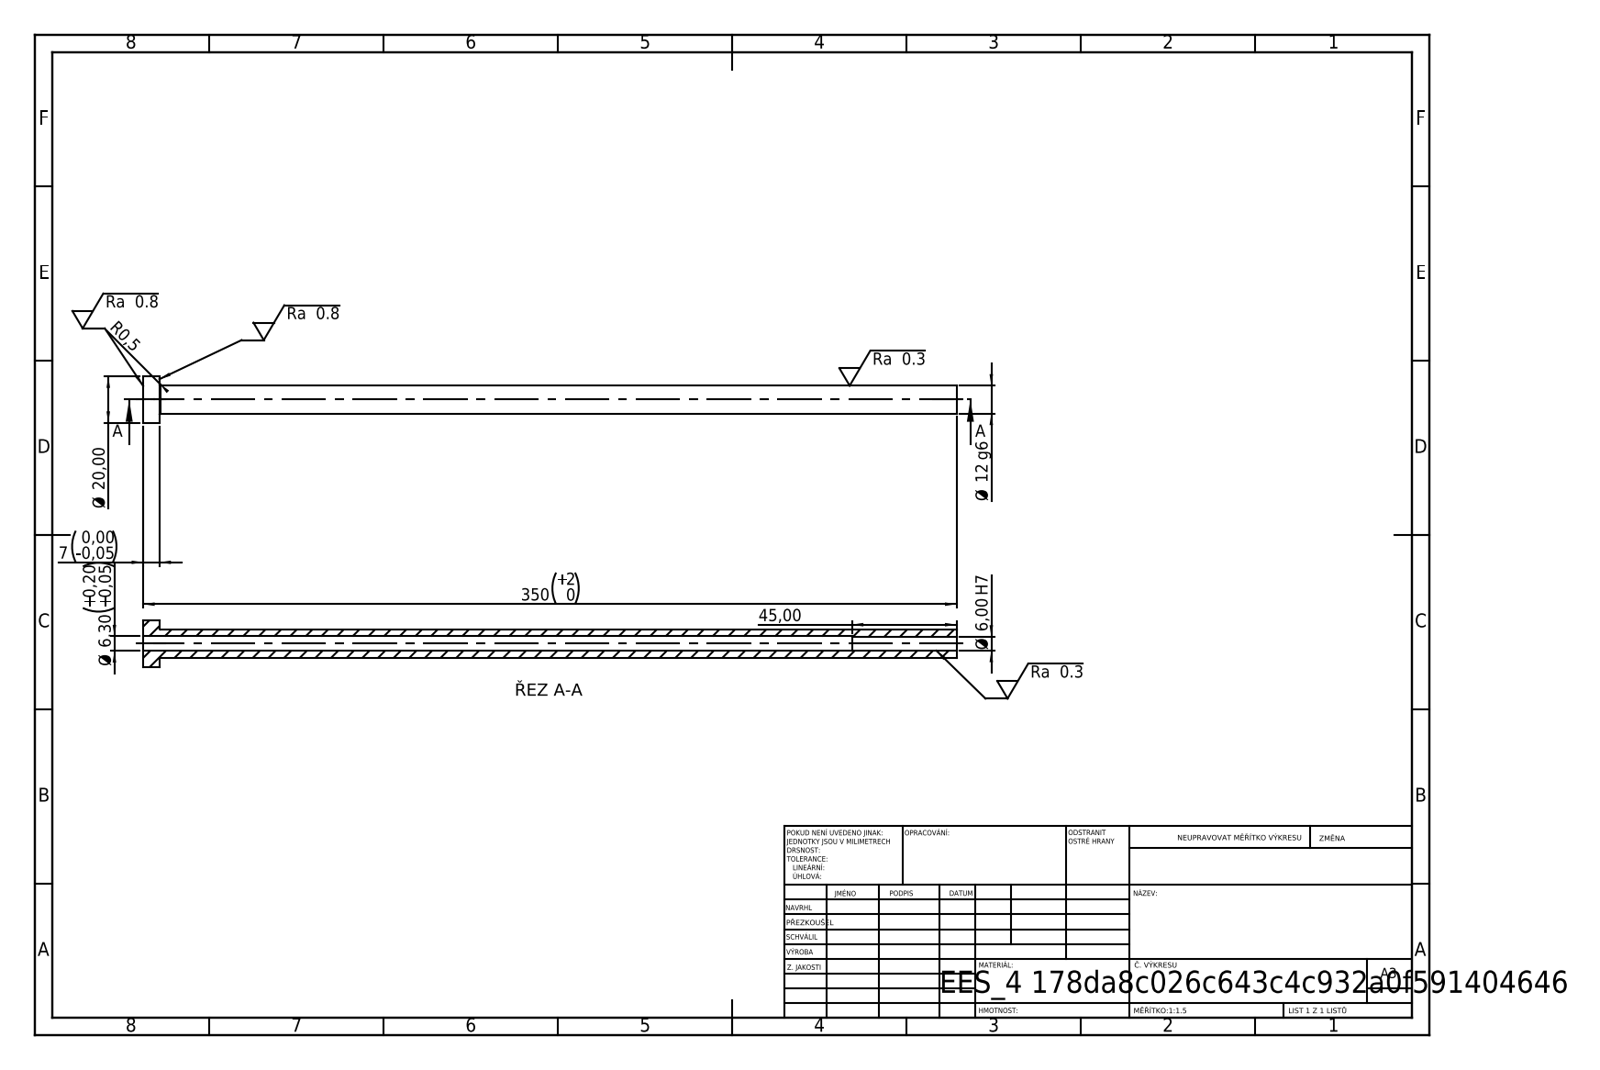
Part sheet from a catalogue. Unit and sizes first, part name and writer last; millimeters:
Units: millimetres
Overall size (bounding box): 350 × 20 × 20
Round holes (diameter × count): ⌀6 ×1, ⌀6.3 ×1
Round bosses / shafts (diameter × count): ⌀20 ×1, ⌀12 ×1
Main face-to-face distances: 7, 350, 343, 305, 298, 45
Volume: 30 214 mm³ · Surface area: 20 819 mm²
Bodies: 1 solid, 14 faces (4 planar, 8 cylindrical, 2 other)
STEP written by: SolidWorks 2019 (CONFIG_CONTROL_DESIGN)
